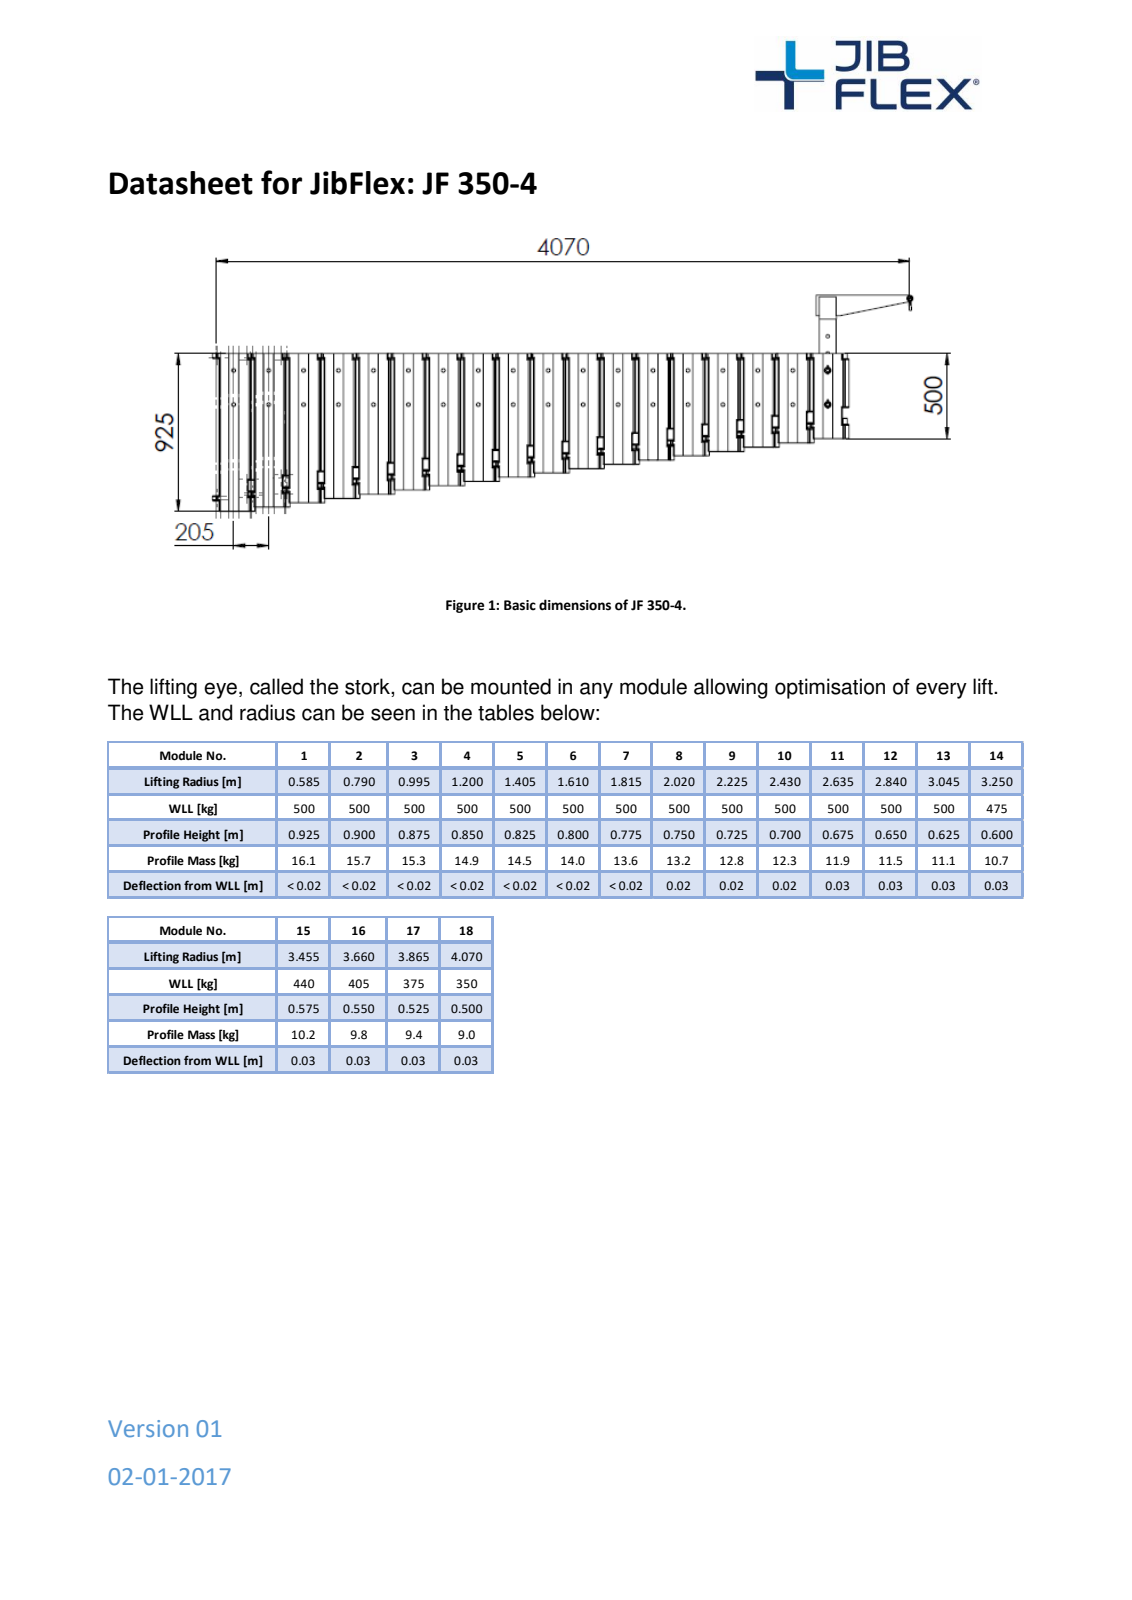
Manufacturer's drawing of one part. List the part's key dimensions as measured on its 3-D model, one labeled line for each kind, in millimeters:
Part name (STEP PRODUCT): 911410214; 911410205; 911410207; 911410204 (+8 more)
STEP written by: SolidWorks 2016 (CONFIG_CONTROL_DESIGN)
Units: millimetres
Bodies: 99 solids, 5164 faces (1110 planar, 1808 cylindrical, 2246 other)
Overall size (bounding box): 4089.5 × 925 × 125.01
Volume: 80 920 000 mm³ · Surface area: 13 400 000 mm²
Round holes (diameter × count): ⌀20.15 ×36, ⌀25 ×36, ⌀28 ×19, ⌀4 ×18, ⌀20 ×18, ⌀4.5 ×1, ⌀13.8 ×1, ⌀17 ×1, ⌀17.4 ×1
Round bosses / shafts (diameter × count): ⌀35 ×19, ⌀28 ×18, ⌀45 ×17, ⌀13 ×2, ⌀25 ×1, ⌀16 ×1, ⌀12 ×1
Partial cylindrical surfaces — rounded edges, fillets, slot ends (radius × count): R6 ×364, R10 ×72, R18 ×72, R37.61 ×36, R24.5 ×19, R52.5 ×18, R62.5 ×18, R5 ×6
Main face-to-face distances: 94.3, 188.6, 282.9, 377.2, 471.5, 407.92, 313.62, 219.32, 125.02, 502.22
Hole centre spacings: 205, 410, 615, 820, 1025, 1230, 1435, 286.4
